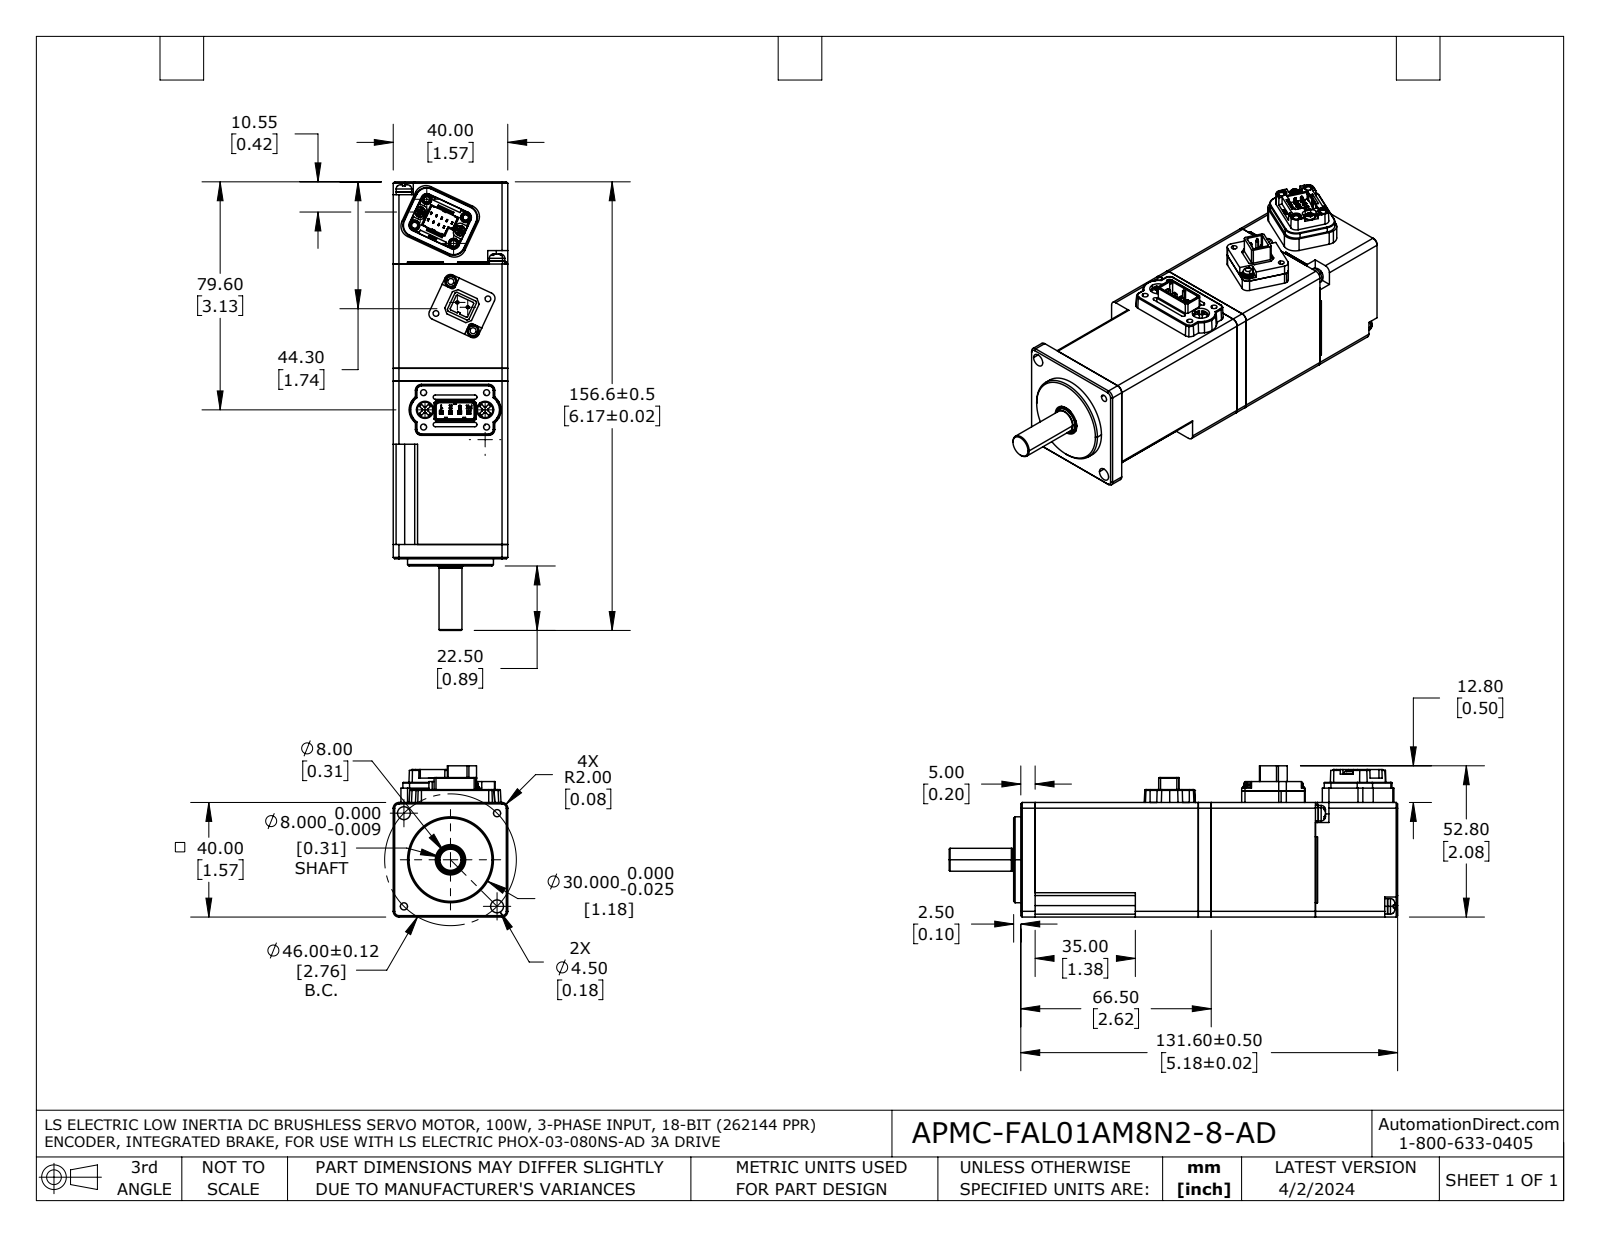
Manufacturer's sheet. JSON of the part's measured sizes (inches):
{"part_name": "APMC-FAL01AM8N2-8-AD", "step_written_by": "SolidWorks 2021 (AUTOMOTIVE_DESIGN)", "units": "inches", "bodies": {"solids": 33, "faces": 1610, "planar": 985, "cylindrical": 429, "other": 196}, "overall_size": [6.165, 2.079, 1.575], "volume_in3": 13.14, "surface_area_in2": 85.33, "round_holes": [[0.083, 10], [0.118, 6], [0.079, 4], [0.142, 4], [0.039, 2], [0.098, 2], [0.177, 2], [0.236, 2], [0.13, 1], [0.134, 1], [0.417, 1], [0.512, 1]], "round_bosses_or_shafts": [[0.213, 6], [0.165, 2], [0.142, 2], [0.138, 2], [0.087, 2], [0.079, 2], [0.035, 2], [1.181, 1]], "partial_cylinders_radius": [[0.008, 20], [0.039, 10], [0.006, 9], [0.079, 8], [0.018, 7], [0.004, 6], [0.059, 6], [0.012, 4]], "face_to_face_distances": [1.575, 0.177, 1.61, 0.028, 1.433, 3.854, 2.421, 2.244, 1.461, 1.638], "hole_center_spacings": [0.237, 0.63, 0.879, 0.906, 1.28, 0.081, 0.197, 0.197]}
